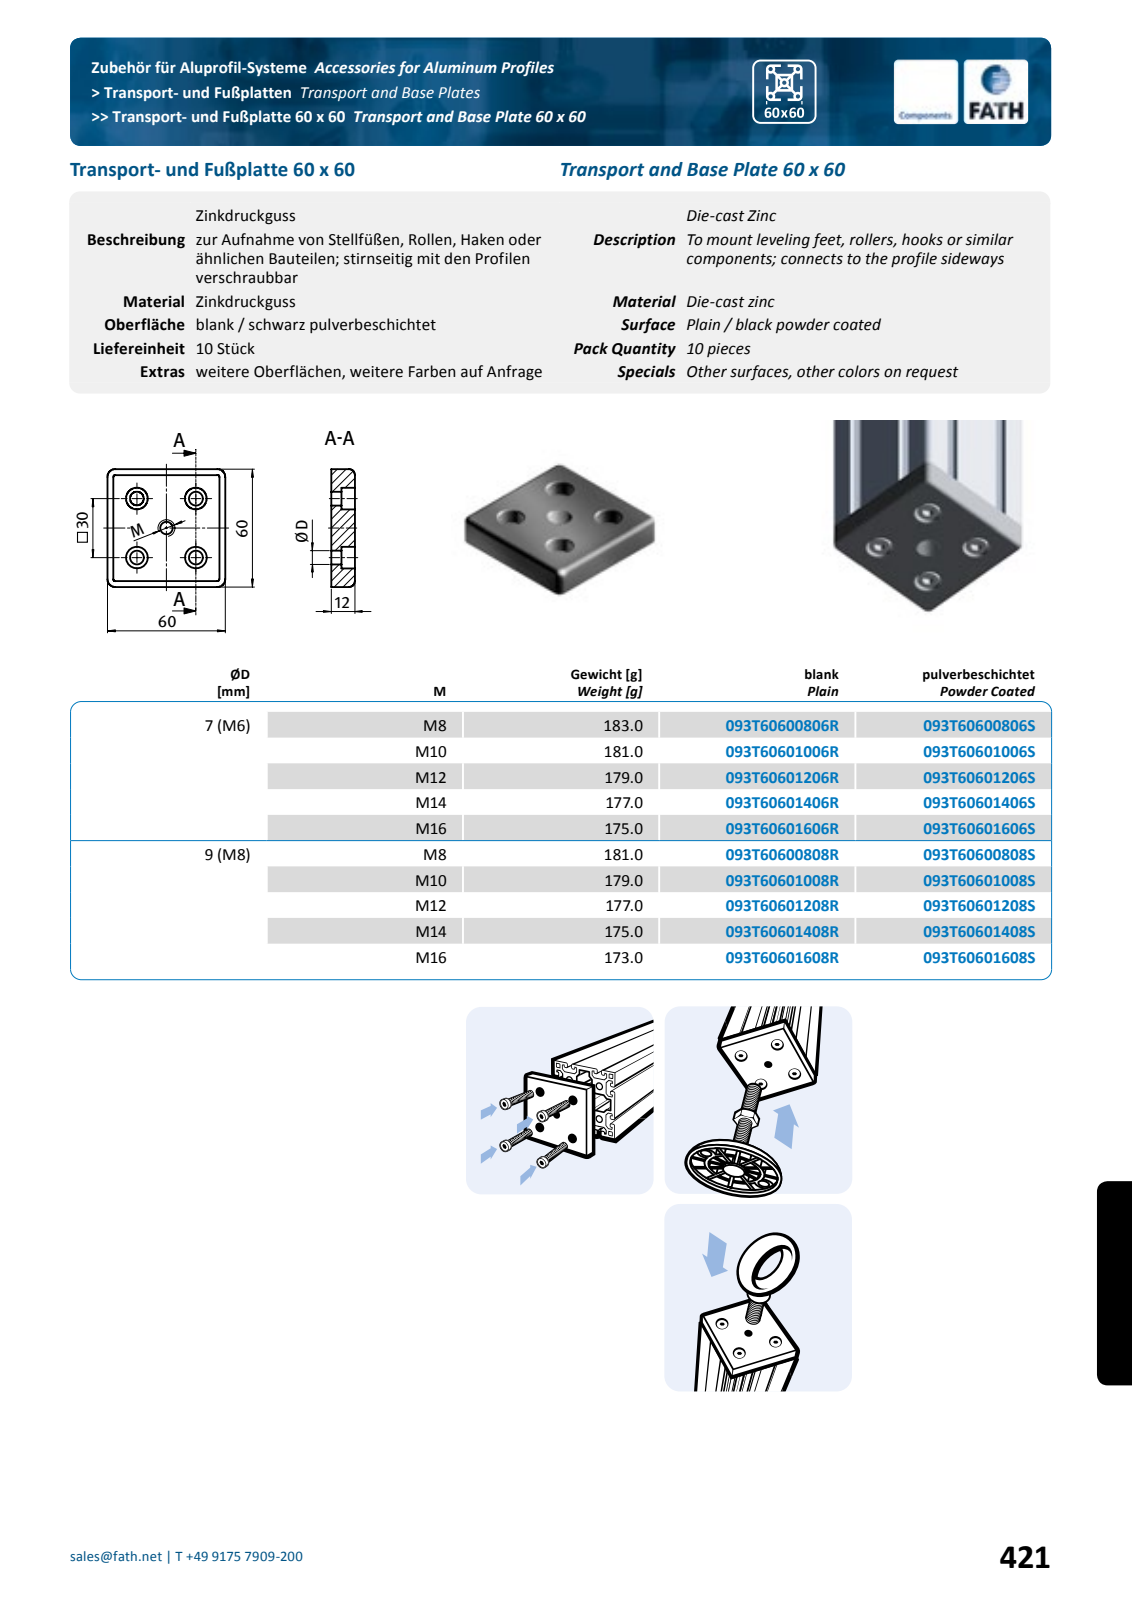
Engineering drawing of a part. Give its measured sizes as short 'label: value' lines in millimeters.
name: fath_093t60601208s
written by: Spatial InterOp 3D (automotive_design)
unit: mm
bodies: 1 solid, 193 faces (26 planar, 100 cylindrical, 67 other)
size: 60 × 60 × 12
volume: 24 556 mm³; area: 15 618 mm²
holes: 4× ⌀9, 4× ⌀15, 1× ⌀10.1
bosses: 4× ⌀20
rounds: 16× R0.5, 16× R1, 8× R2, 1× R11
face distances: 3, 12, 57, 9, 60, 54, 6, 5
hole spacings: 21.21, 30, 42.43
